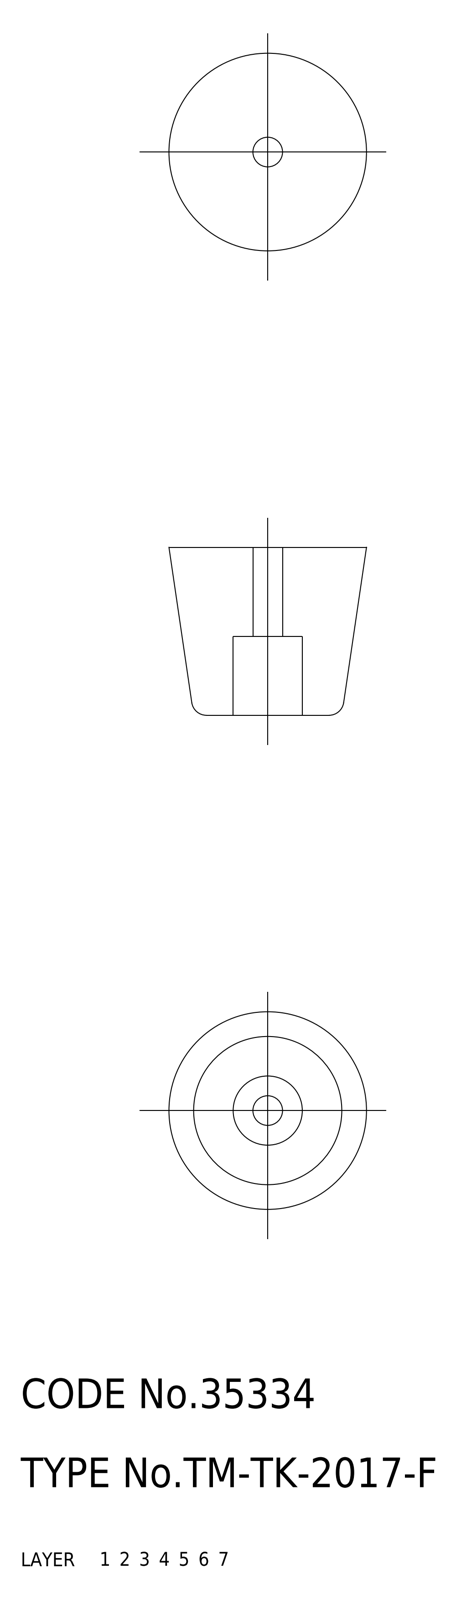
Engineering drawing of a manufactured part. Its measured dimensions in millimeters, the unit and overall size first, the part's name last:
Units: millimetres
Overall size (bounding box): 20 × 20 × 17
Round holes (diameter × count): ⌀3 ×1, ⌀3.5 ×1, ⌀7 ×1, ⌀9 ×1
Main face-to-face distances: 8.5, 17, 8, 0.5, 9
Volume: 3 730 mm³ · Surface area: 1 857 mm²
Bodies: 2 solids, 23 faces (7 planar, 12 cylindrical, 4 other)
Part name (STEP PRODUCT): TM_TK_2017_F; washer; rubber foot
STEP written by: SolidWorks 2015 (AUTOMOTIVE_DESIGN)
